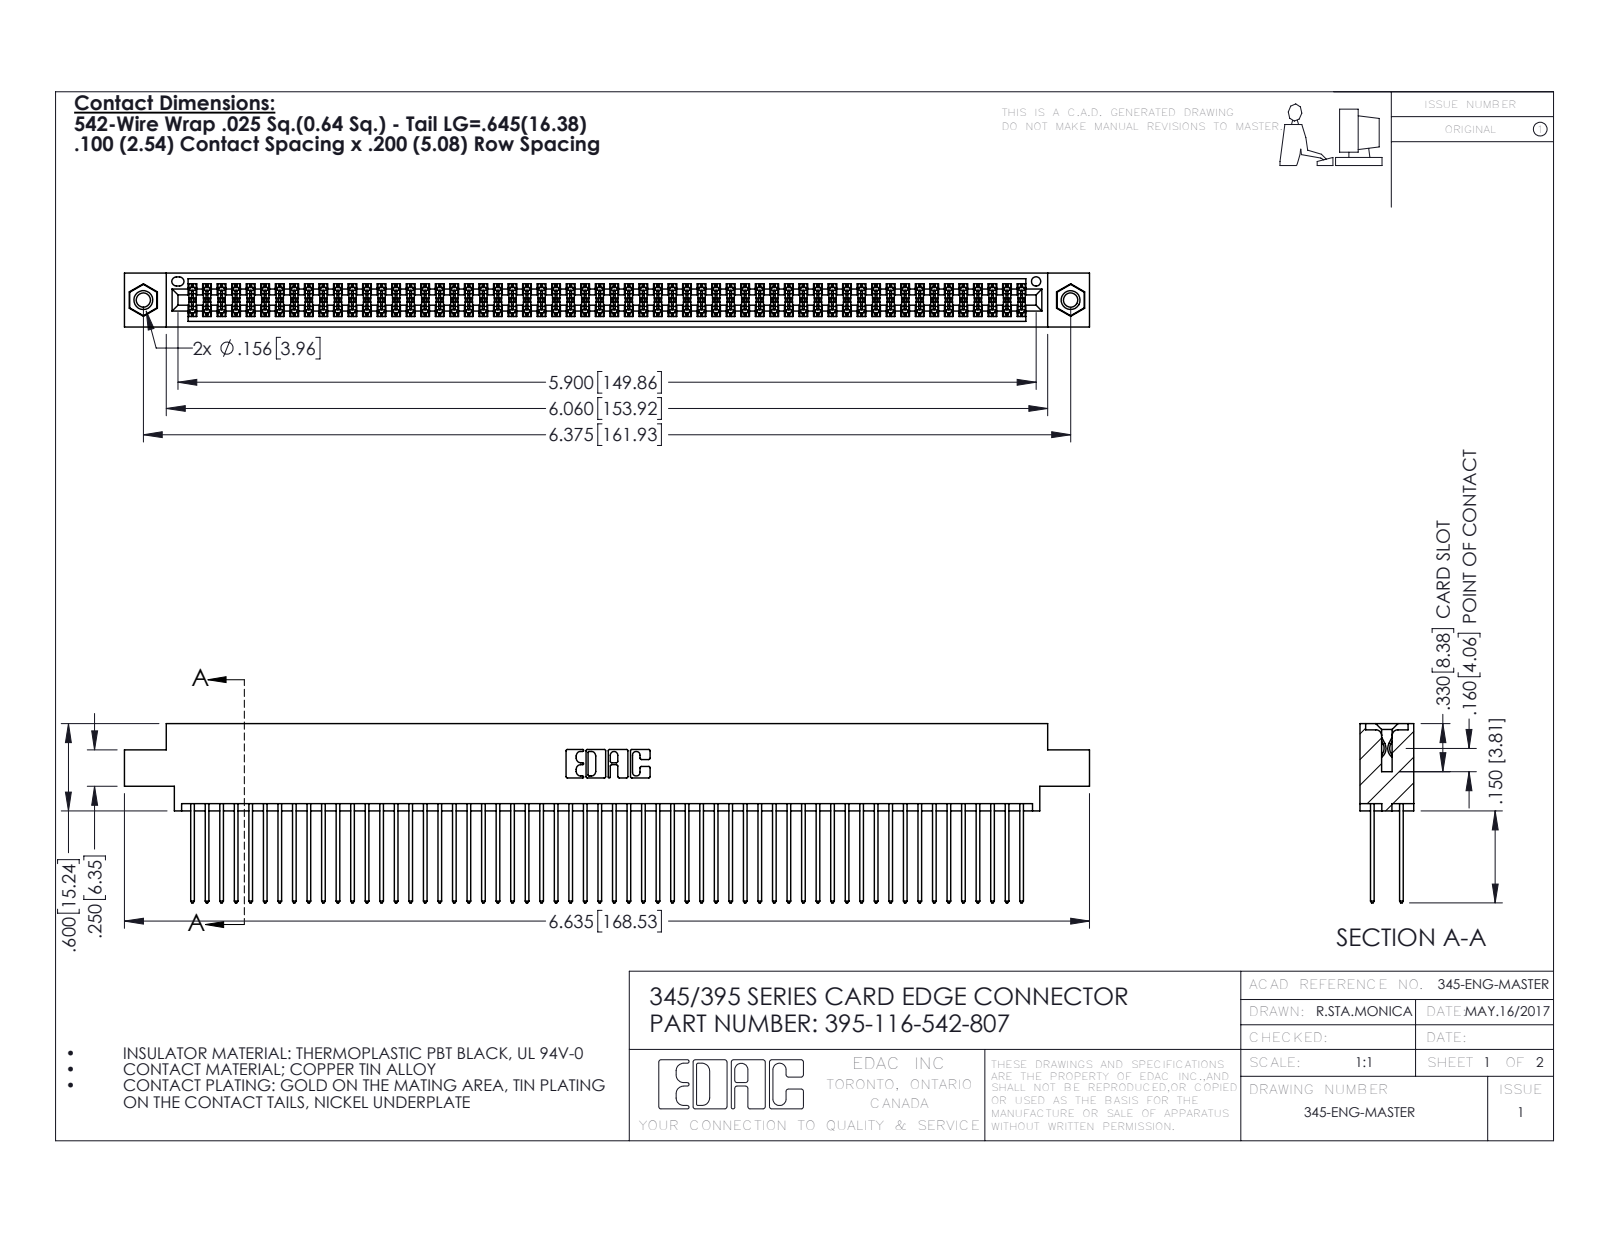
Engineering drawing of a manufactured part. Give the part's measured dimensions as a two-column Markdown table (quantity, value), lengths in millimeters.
| quantity | value |
| --- | --- |
| part name | 345 Part_0.170 Offset - 0.156 Dia-TI; 345-250-001_345-250-005-103; 345-292-001_345-293-142; 395-116-542-807 |
| STEP written by | SolidWorks 2016 (CONFIG_CONTROL_DESIGN) |
| units | millimeters |
| bodies | 119 solids, 5990 faces (3944 planar, 2030 cylindrical, 16 other) |
| overall size | 168.5 × 31.3 × 9.4 |
| volume | 16 930 mm³ |
| surface area | 28 040 mm² |
| round holes (diameter × count) | 2.5 × 2, 3.2 × 2, 4 × 2, 1.6 × 1 |
| round bosses / shafts (diameter × count) | 3.9 × 2 |
| partial cylindrical surfaces (radius × count) | 0.2 × 174, 0.3 × 116, 0.3 × 22, 0.2 × 6, 0.8 × 6, 0.7 × 3, 0.4 × 2, 0.5 × 2 |
| main face-to-face distances | 1.8, 7.6, 5.1, 2.5, 6.9, 0.6, 9.4, 5.7, 4.4, 3.8 |
| hole center spacings | 6.9, 155.9, 161.9 |
